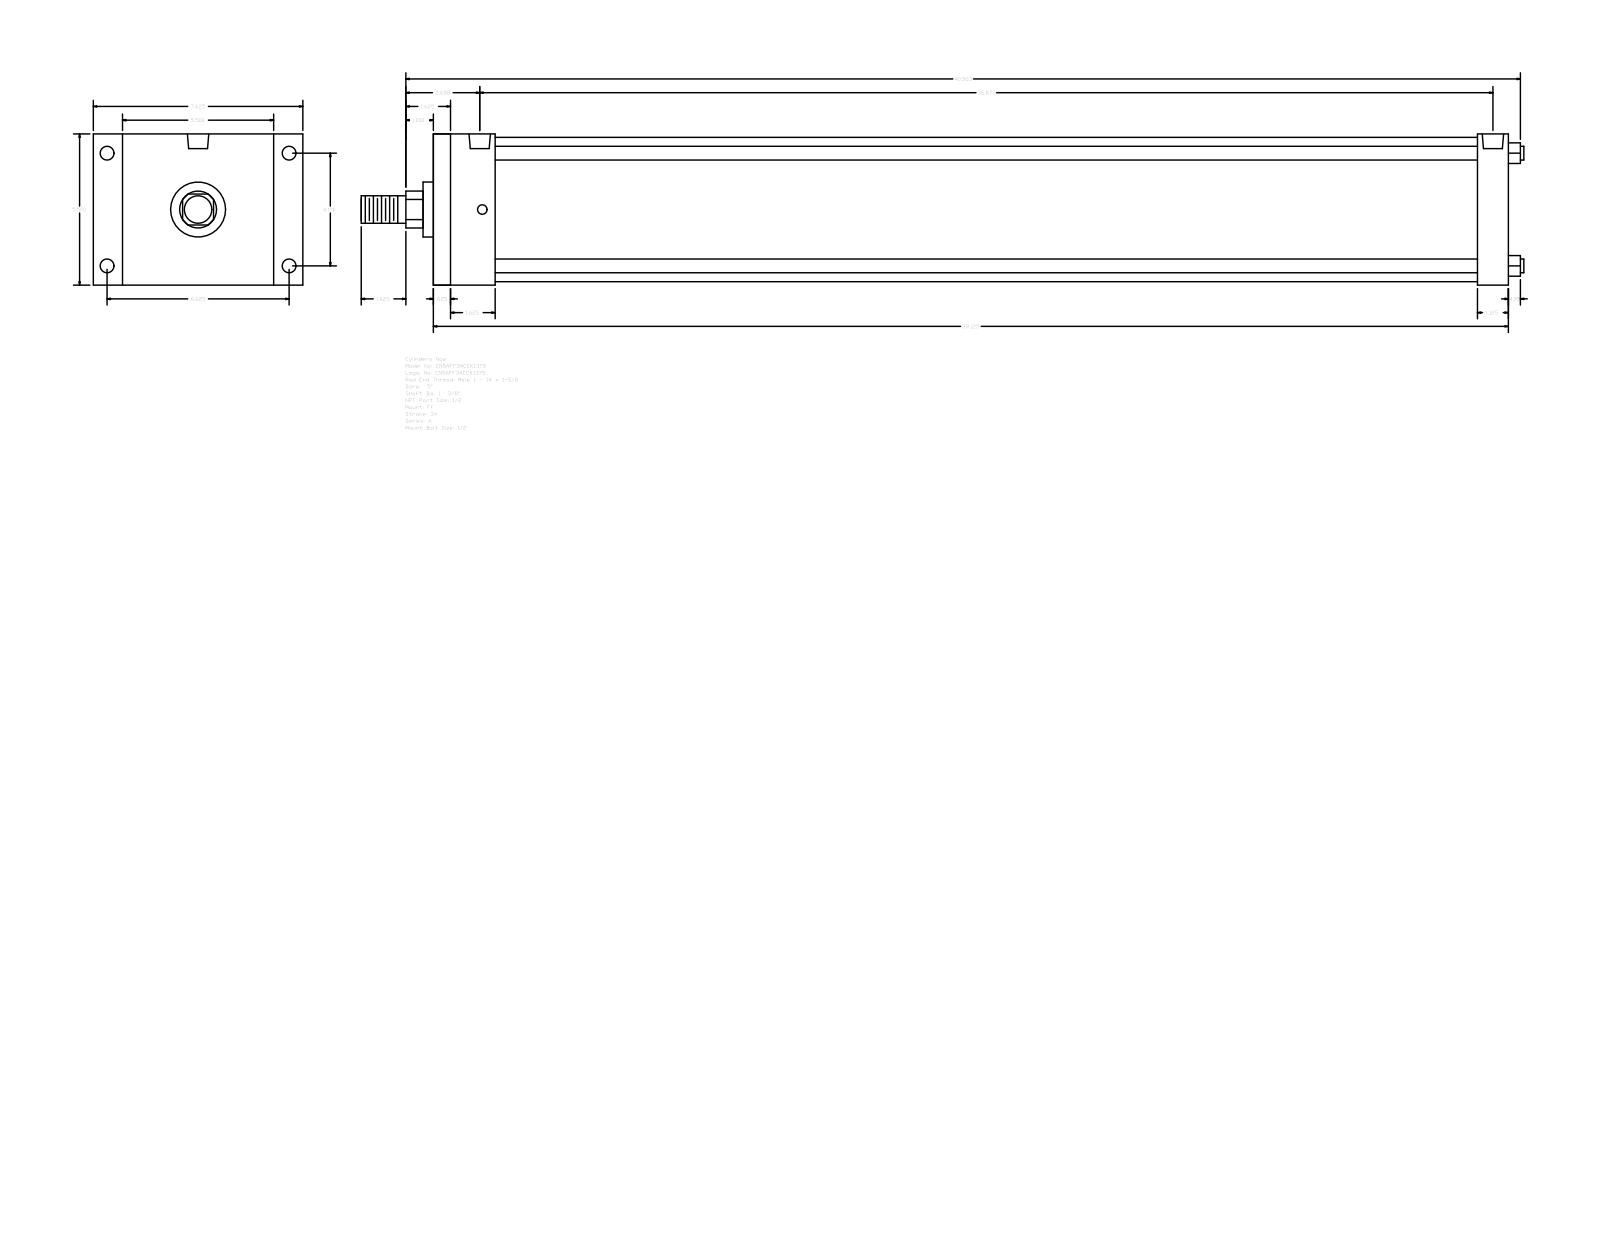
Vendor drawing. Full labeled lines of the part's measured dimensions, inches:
Part name (STEP PRODUCT): A_FF__0500_1.375
STEP written by: GSSL Pune (CONFIG_CONTROL_DESIGN)
Units: inches
Bodies: 0 solids, 92 faces (64 planar, 28 cylindrical, 0 other)
Overall size (bounding box): 42.313 × 7.625 × 5.5
Round holes (diameter × count): ⌀0.344 ×4, ⌀0.5 ×4, ⌀0.778 ×2
Round bosses / shafts (diameter × count): ⌀0.5 ×4, ⌀5.25 ×1, ⌀2 ×1, ⌀1.375 ×1, ⌀1 ×1
Partial cylindrical surfaces — rounded edges, fillets, slot ends (radius × count): R0.672 ×1
Main face-to-face distances: 5.5, 39.125, 38.5, 0.625, 2.25, 1.125, 38, 37.375, 1.625, 35.75
Hole centre spacings: 0.094, 4.1, 6.625, 7.791, 36.687, 36.781, 36.875
